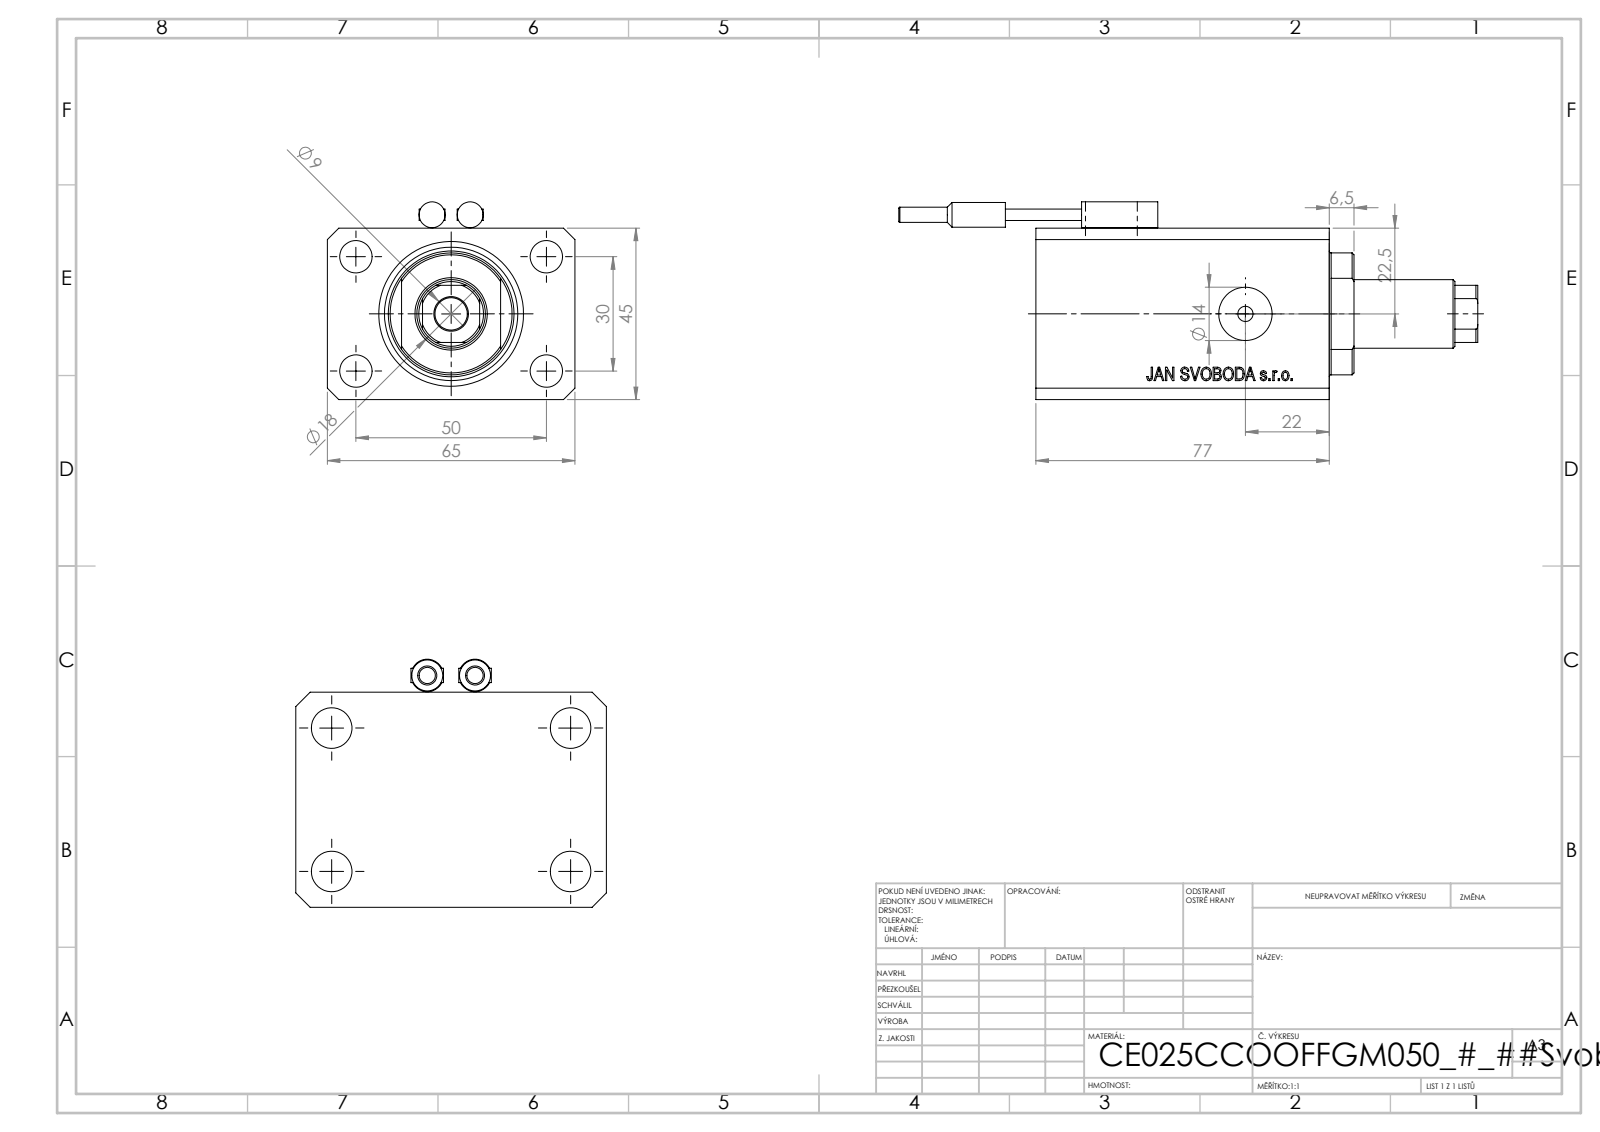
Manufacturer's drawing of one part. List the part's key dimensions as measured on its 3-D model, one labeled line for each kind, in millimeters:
Part name (STEP PRODUCT): SWITCH_V250CE; V250CE_C_Body; V250CE_C_VCP; V250CE_VC_C
STEP written by: SolidWorks 2019 (CONFIG_CONTROL_DESIGN)
Units: millimetres
Bodies: 5 solids, 905 faces (457 planar, 48 cylindrical, 400 other)
Overall size (bounding box): 152 × 65 × 51.9
Volume: 220 347 mm³ · Surface area: 52 877 mm²
Round holes (diameter × count): ⌀8.5 ×5, ⌀4 ×2, ⌀14 ×2, ⌀18 ×1, ⌀25 ×1, ⌀38 ×1
Round bosses / shafts (diameter × count): ⌀6.8 ×2, ⌀6.5 ×2, ⌀4 ×2
Partial cylindrical surfaces — rounded edges, fillets, slot ends (radius × count): R8.5 ×1, R16 ×1
Main face-to-face distances: 45, 65, 77, 51.9, 25.1, 32, 19.9, 73.52, 6.5, 51.5
Hole centre spacings: 29.15, 30, 50, 58.31, 33
